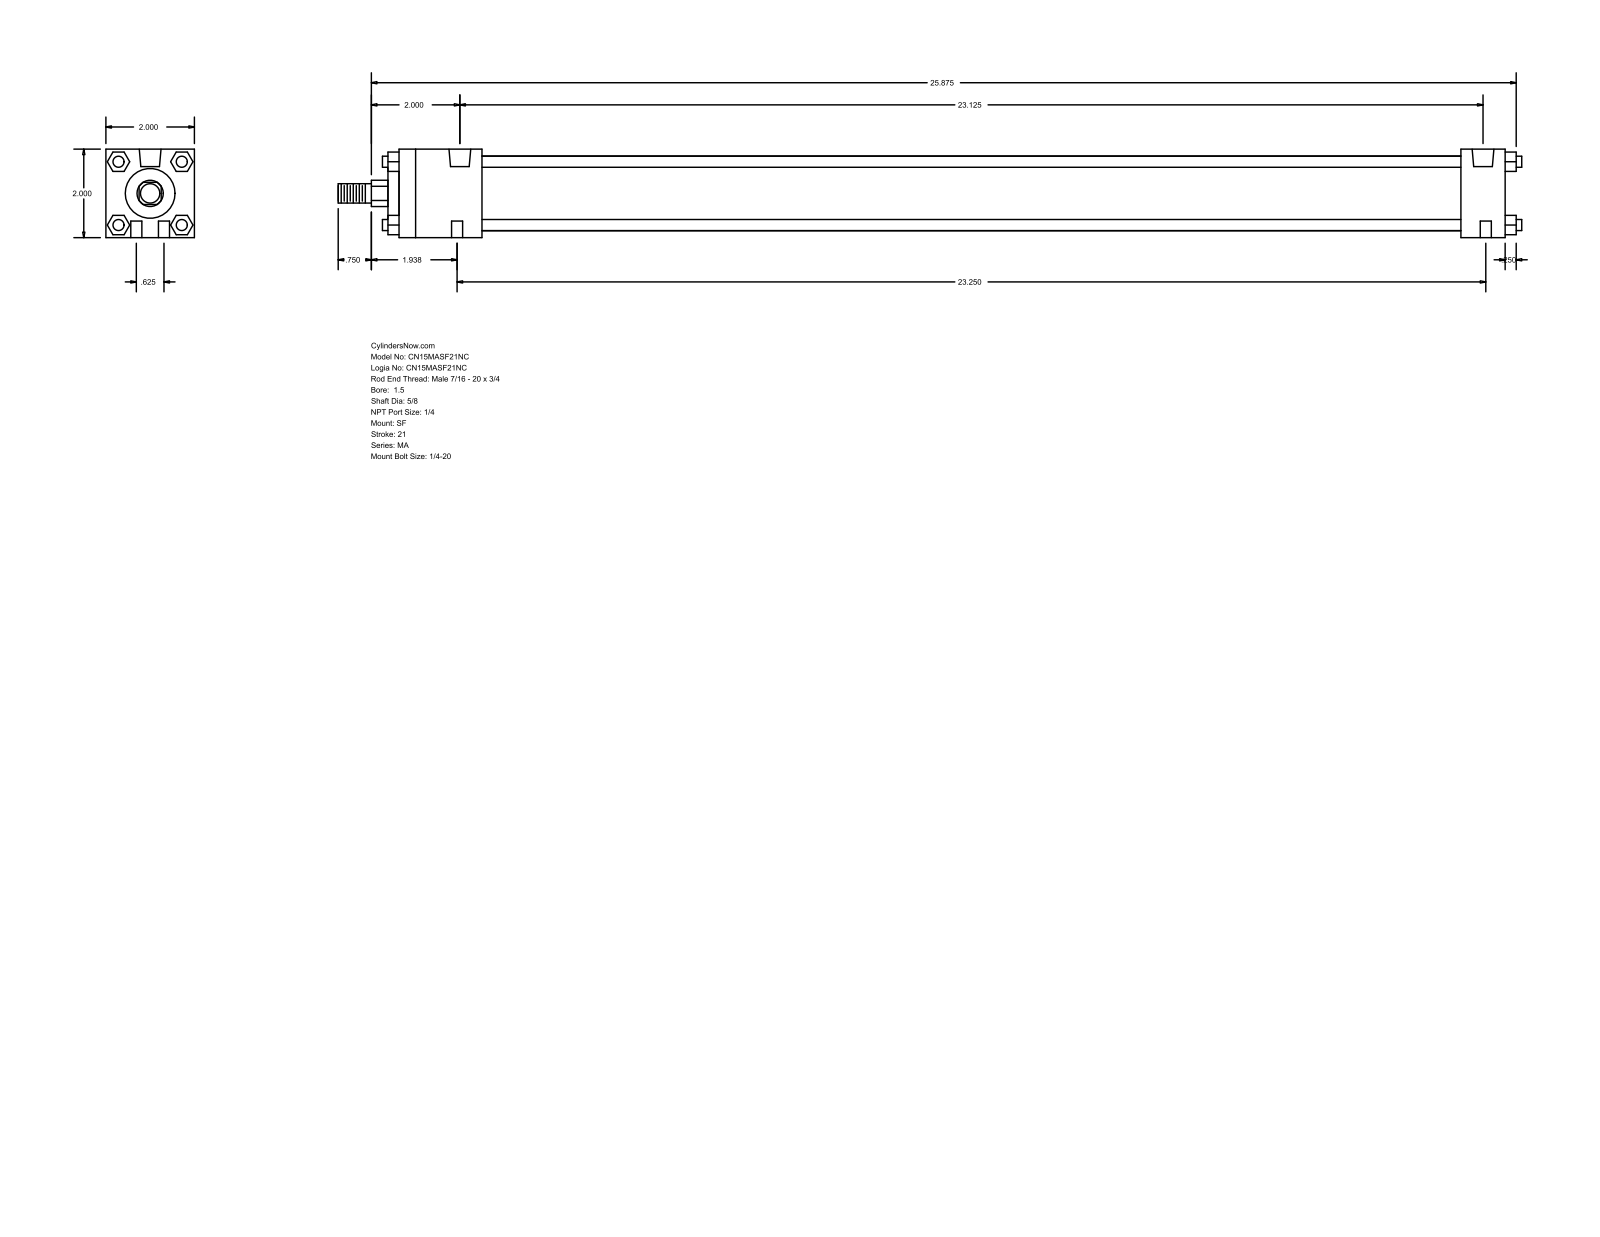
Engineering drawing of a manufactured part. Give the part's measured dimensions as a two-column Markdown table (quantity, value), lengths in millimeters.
| quantity | value |
| --- | --- |
| part name | MA_SF__0150_0.625 |
| STEP written by | GSSL Pune (CONFIG_CONTROL_DESIGN) |
| units | millimeters |
| bodies | 0 solids, 124 faces (94 planar, 30 cylindrical, 0 other) |
| overall size | 679.45 × 50.8 × 50.8 |
| round holes (diameter × count) | 6.35 × 4, 7.94 × 2, 12.49 × 2 |
| round bosses / shafts (diameter × count) | 6.35 × 4, 42.93 × 1, 28.57 × 1, 15.88 × 1, 11.11 × 1 |
| partial cylindrical surfaces (radius × count) | 7.54 × 1 |
| main face-to-face distances | 50.8, 635, 6.35, 25.4, 641.35, 47.62, 609.6, 561.98, 587.38, 53.97 |
| hole center spacings | 8.1, 589.01, 15.88, 587.37, 590.55, 590.76 |
